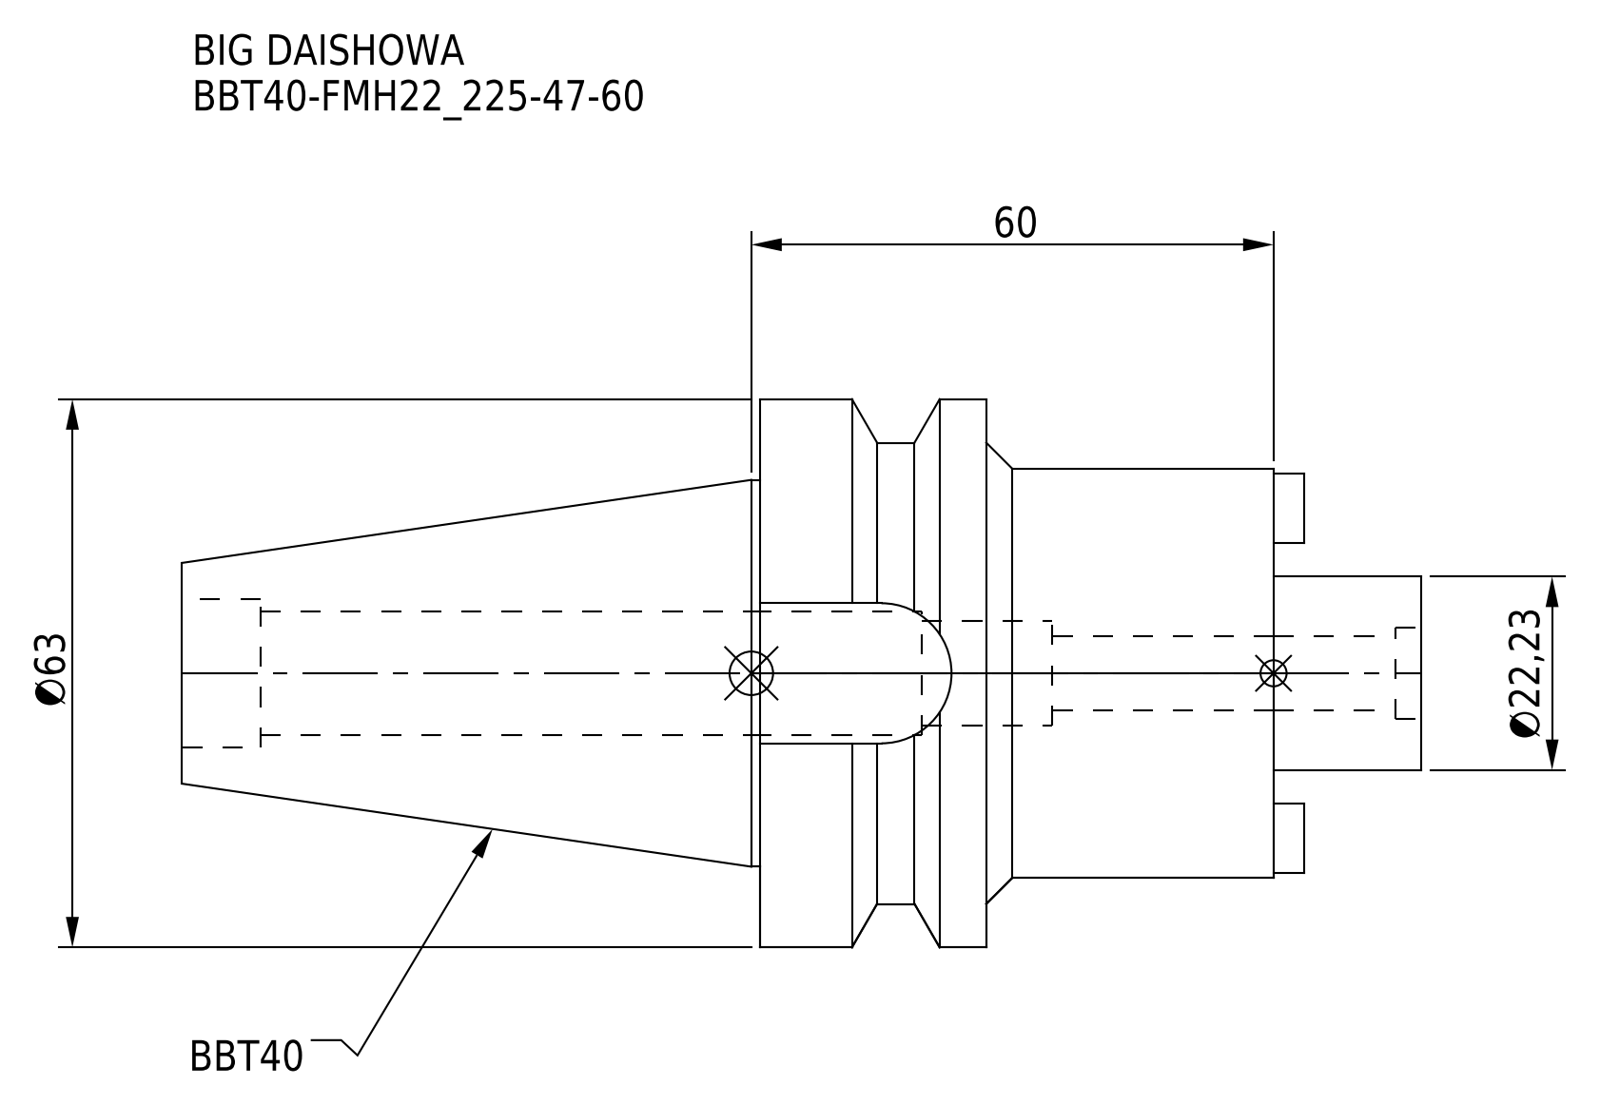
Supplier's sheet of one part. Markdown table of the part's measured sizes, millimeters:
| quantity | value |
| --- | --- |
| part name | BBT40-FMH22_225-47-60 |
| STEP written by | CREO PARAMETRIC BY PTC INC, 2016380 (AUTOMOTIVE_DESIGN) |
| units | millimeters |
| bodies | 1 solid, 61 faces (25 planar, 28 cylindrical, 8 other) |
| overall size | 142.4 × 63 × 63 |
| volume | 182 298 mm³ |
| surface area | 30 322 mm² |
| round holes (diameter × count) | 8.5 × 1, 10.5 × 1, 12 × 1, 14.2 × 1, 17 × 1 |
| round bosses / shafts (diameter × count) | 63 × 1, 53 × 1, 47 × 1, 44.45 × 1, 22.23 × 1 |
| partial cylindrical surfaces (radius × count) | 8.05 × 1 |
| main face-to-face distances | 59, 33, 26, 76, 45, 17, 50, 142.4, 125.4, 92.4 |
